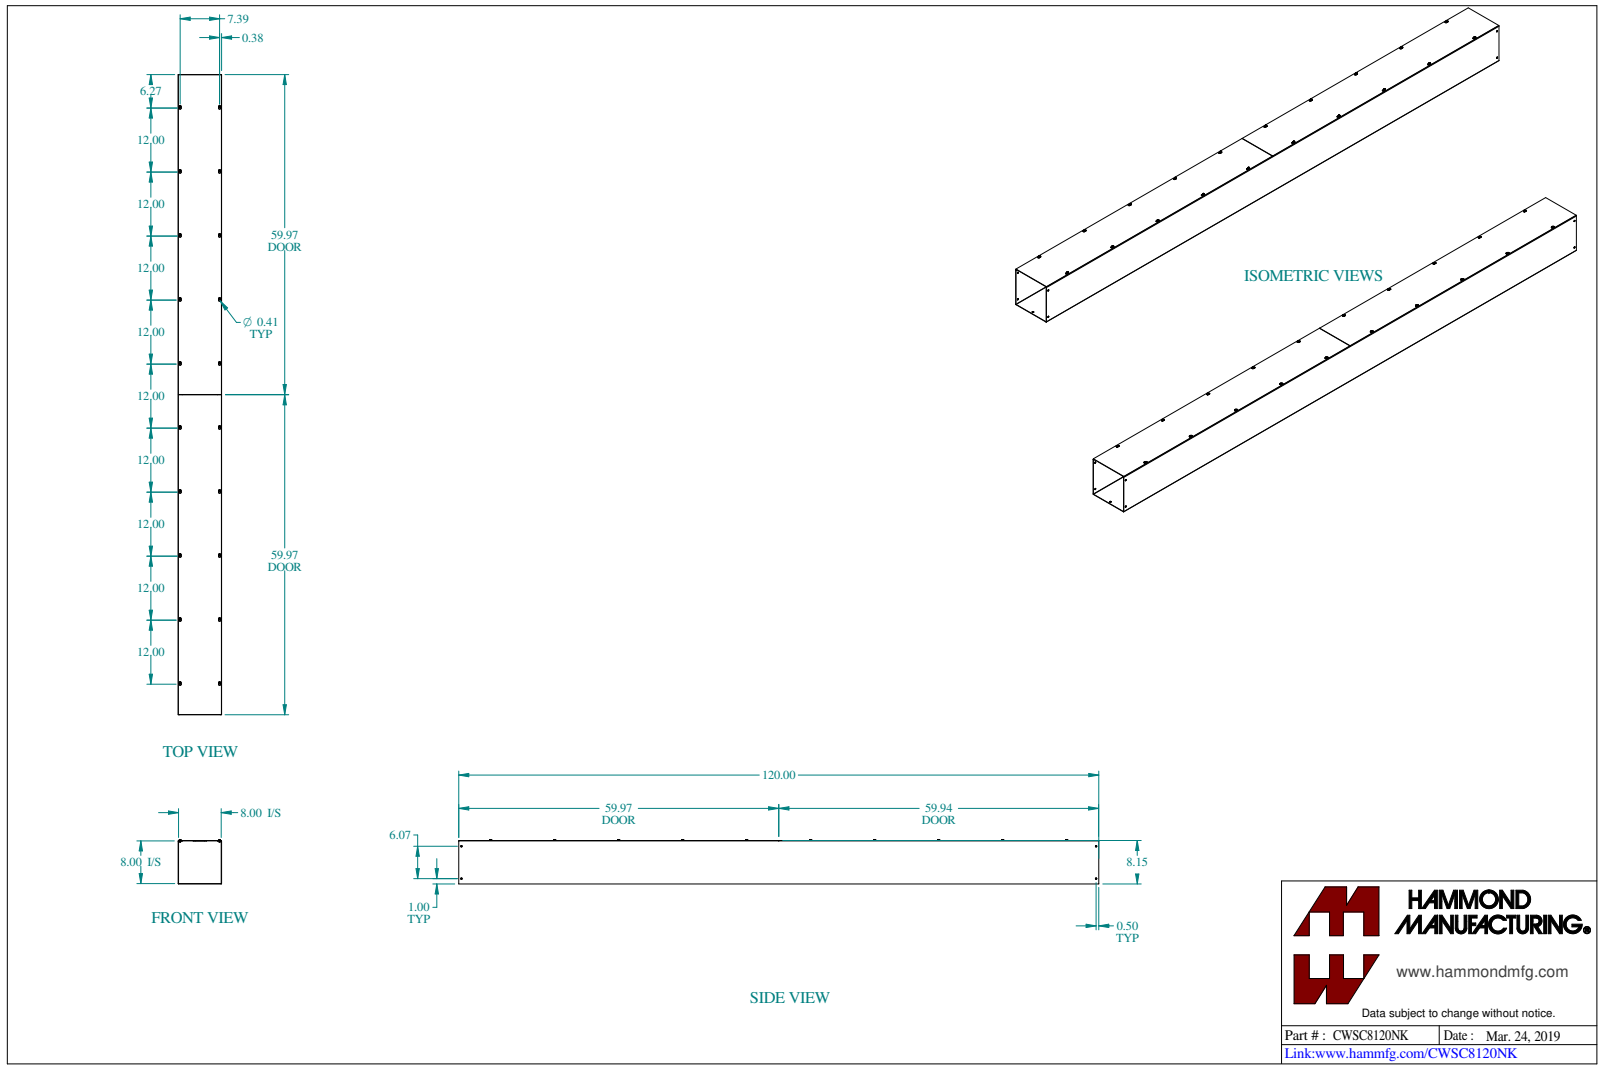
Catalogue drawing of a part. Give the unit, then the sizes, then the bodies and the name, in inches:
Units: inches
Overall size (bounding box): 120 × 8.325 × 8.144
Round holes (diameter × count): ⌀0.177 ×20, ⌀0.266 ×4, ⌀0.313 ×2
Round bosses / shafts (diameter × count): ⌀0.375 ×20, ⌀0.19 ×20
Partial cylindrical surfaces — rounded edges, fillets, slot ends (radius × count): R0.125 ×20, R0.203 ×20, R0.036 ×4, R0.108 ×4
Main face-to-face distances: 0.072, 8.072, 8, 0.078, 8.15, 8.078, 8.144, 7.928, 0.15, 0.031
Hole centre spacings: 12, 14.095, 24, 25.113, 36, 36.752, 48, 48.566
Volume: 294.8 in³ · Surface area: 8 072 in²
Bodies: 23 solids, 682 faces (334 planar, 228 cylindrical, 120 other)
Part name (STEP PRODUCT): CWSC8120NK
STEP written by: SolidWorks 2023 (CONFIG_CONTROL_DESIGN)
